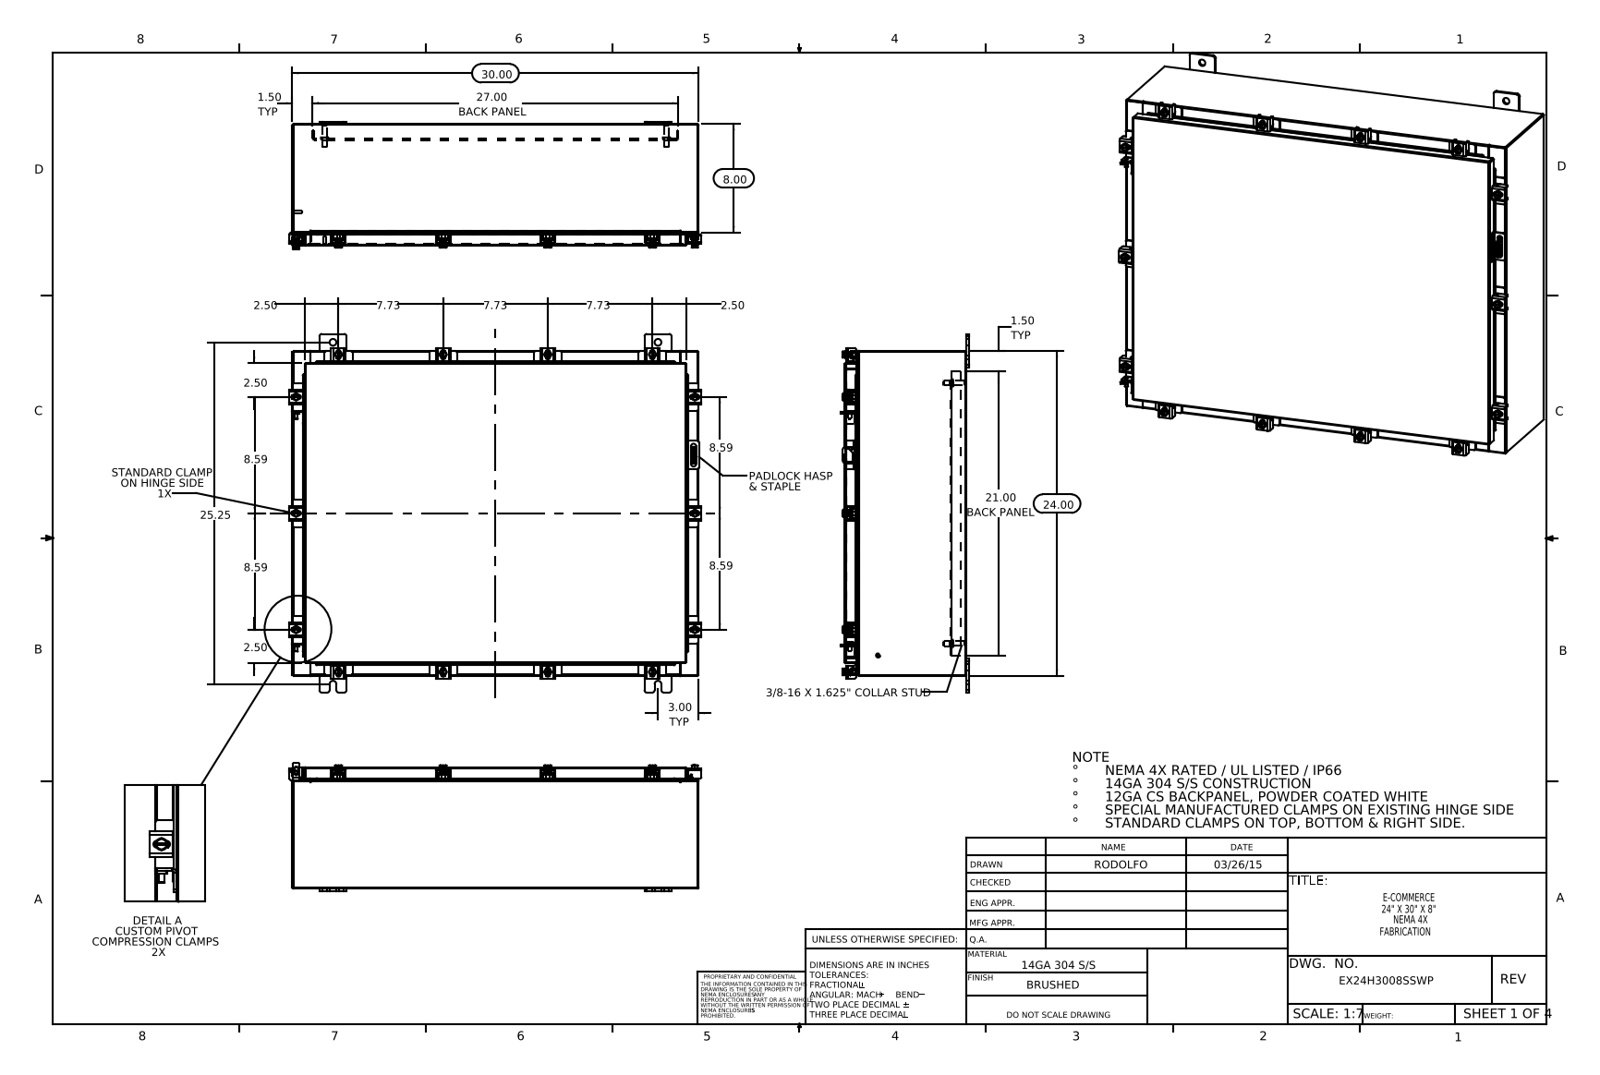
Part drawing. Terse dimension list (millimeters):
name: EX24H3008SSWP Bottom; Quarter-20 CD Stud; Special Clamp Assembly; HW-CLN-NH-20330 (+8 more)
written by: SolidWorks 2014 (CONFIG_CONTROL_DESIGN)
unit: mm
bodies: 91 solids, 2252 faces (1195 planar, 881 cylindrical, 176 other)
size: 772.7 × 673.1 × 240.1
volume: 4 280 000 mm³; area: 4 199 000 mm²
holes: 14× ⌀5.4, 14× ⌀6.6, 8× ⌀12.7, 1× ⌀3.2, 1× ⌀6.4
bosses: 14× ⌀12.7, 14× ⌀6.4, 12× ⌀10.1, 4× ⌀15.9, 4× ⌀9.5, 4× ⌀8.4, 2× ⌀8, 2× ⌀6
rounds: 62× R1.5, 28× R3.6, 26× R3, 24× R0.3, 24× R4.8, 22× R2.2, 20× R2.3, 19× R1.3
face distances: 1.9, 226.1, 228, 224.2, 2.6, 25.4, 27.3, 198.8, 200.7, 29.9
hole spacings: 59.4, 112.5, 465.8, 522.2, 543, 595.7, 673.3, 844.6
